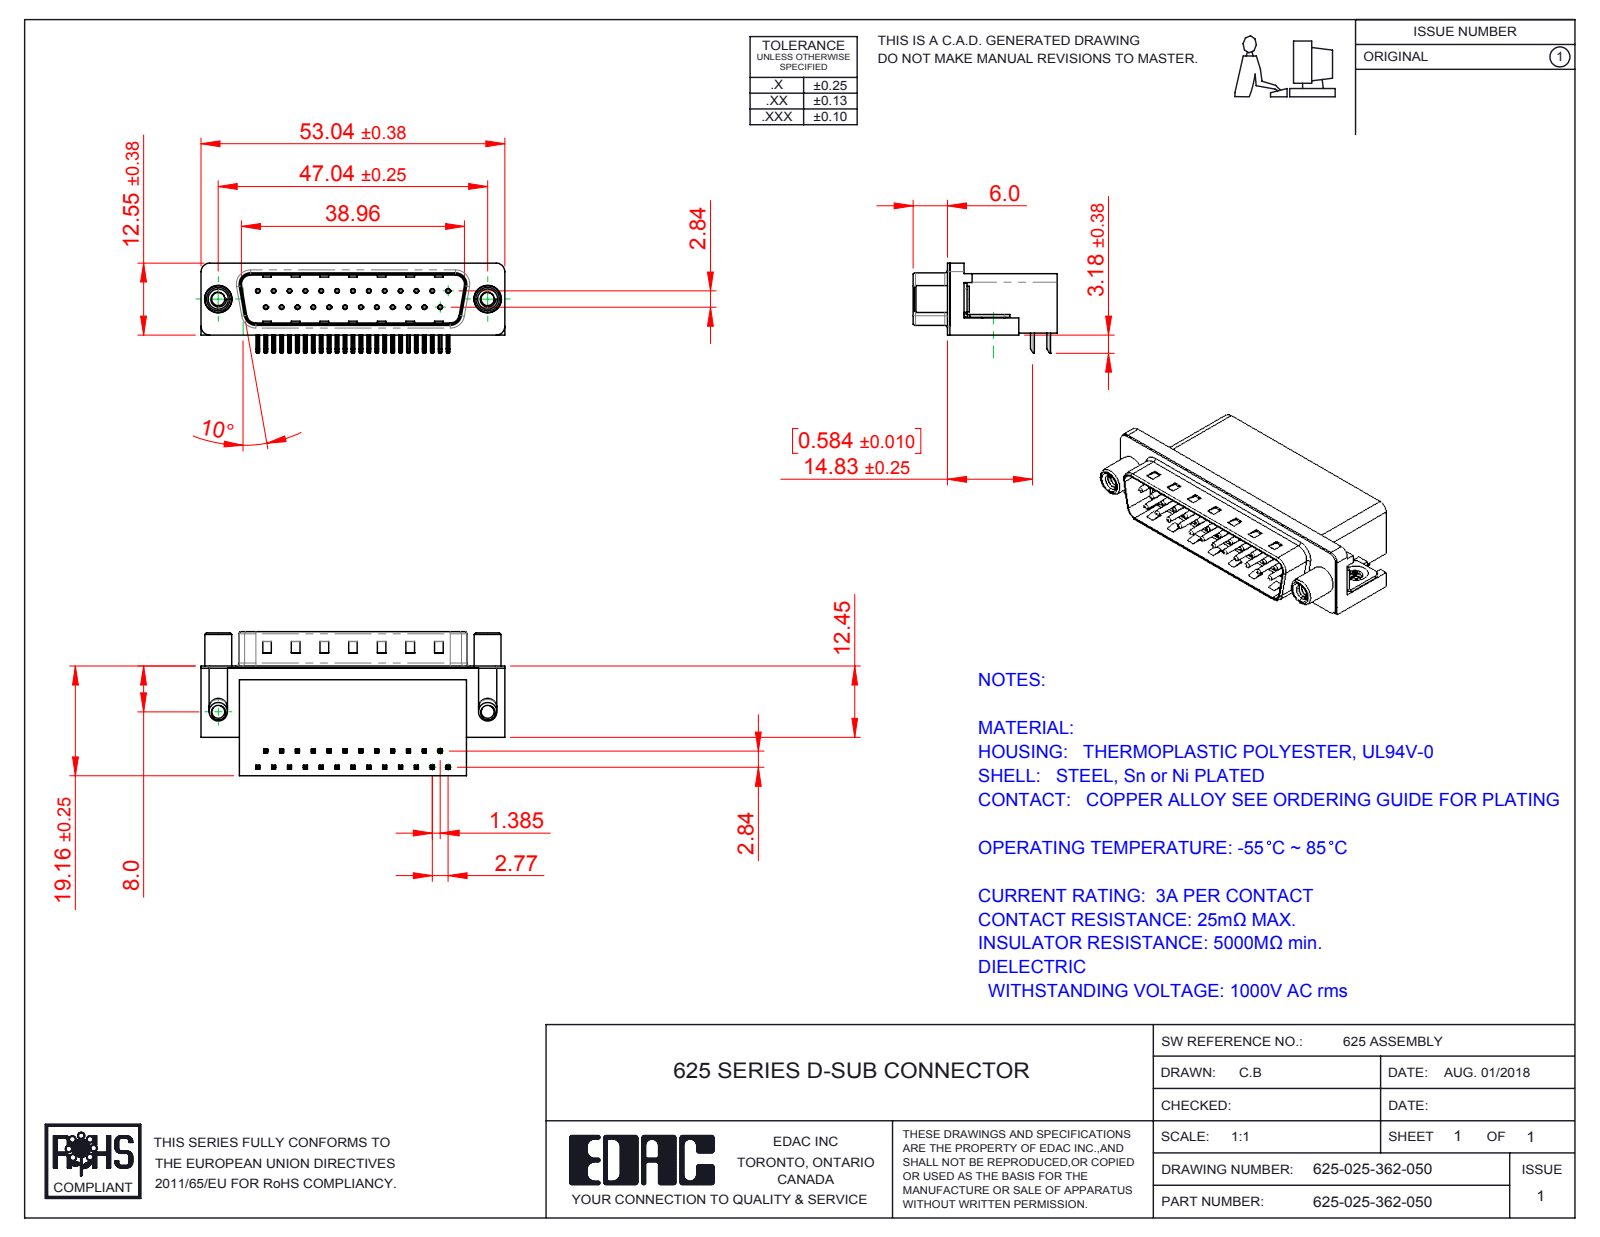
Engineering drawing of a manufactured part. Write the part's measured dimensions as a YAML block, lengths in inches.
part_name: "625 Housing_25 Socket; 625 4-40 Threaded Board Mount; 625-025-362-050; 625 Contact Bottom (+3 more)"
step_written_by: "SolidWorks 2016 (CONFIG_CONTROL_DESIGN)"
units: inches
bodies: {solids: 31, faces: 2291, planar: 1399, cylindrical: 681, other: 211}
overall_size: [2.088, 0.991, 0.619]
volume: 0.565
surface_area: 14.17
round_holes:
  - {diameter: 0.014, count: 25}
  - {diameter: 0.031, count: 25}
  - {diameter: 0.089, count: 2}
  - {diameter: 0.091, count: 2}
  - {diameter: 0.122, count: 2}
  - {diameter: 0.157, count: 2}
  - {diameter: 0.189, count: 2}
  - {diameter: 0.197, count: 2}
round_bosses_or_shafts:
  - {diameter: 0.03, count: 25}
  - {diameter: 0.193, count: 2}
  - {diameter: 0.185, count: 2}
  - {diameter: 0.177, count: 2}
  - {diameter: 0.152, count: 2}
  - {diameter: 0.128, count: 2}
partial_cylinders:
  - {radius: 0.01, count: 100}
  - {radius: 0.005, count: 50}
  - {radius: 0.039, count: 16}
  - {radius: 0.02, count: 9}
  - {radius: 0.063, count: 8}
  - {radius: 0.059, count: 7}
  - {radius: 0.035, count: 4}
  - {radius: 0.079, count: 4}
face_to_face_distances: [0.016, 0.407, 0.739, 0.083, 0.345, 0.412, 0.428, 0.067, 0.754, 0.114]
hole_center_spacings: [0.124, 0.109, 0.436, 0.218, 0.327, 0.198, 0.545, 0.294]
